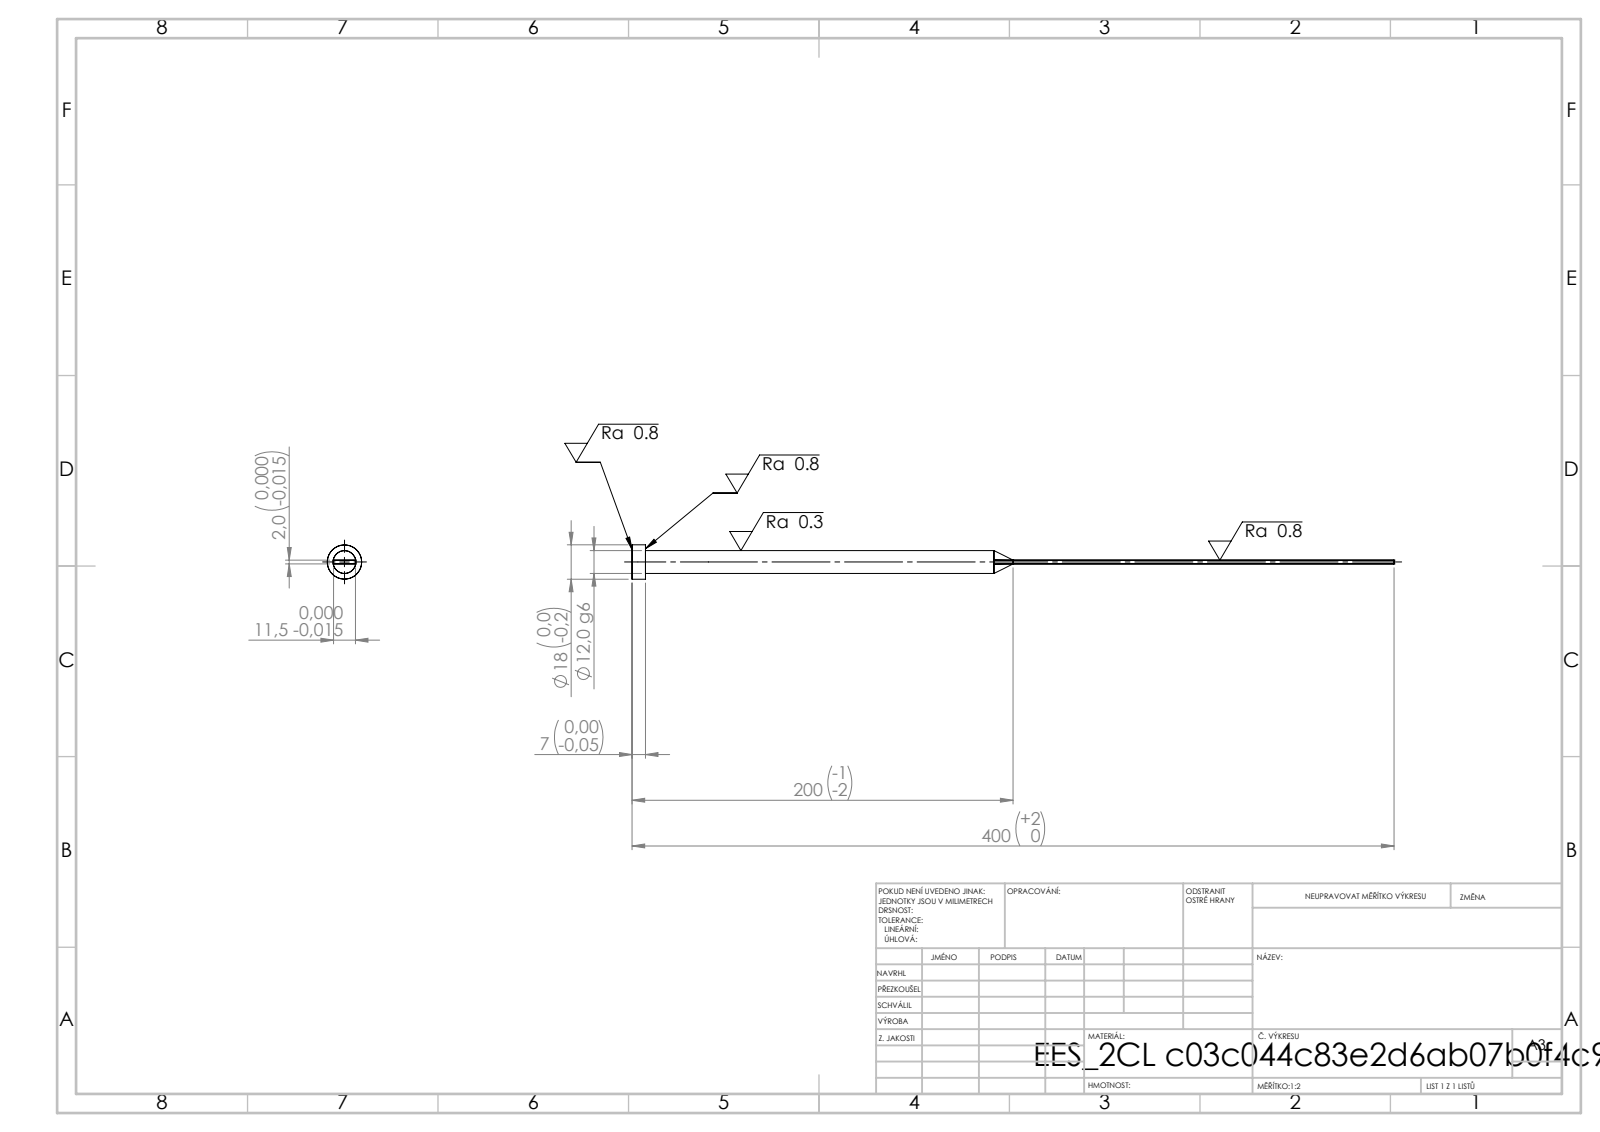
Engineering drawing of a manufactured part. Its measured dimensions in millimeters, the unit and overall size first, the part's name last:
Units: millimetres
Overall size (bounding box): 400 × 18 × 18
Round bosses / shafts (diameter × count): ⌀18 ×1, ⌀12 ×1
Main face-to-face distances: 2, 11.5, 7, 400, 393
Volume: 27 724 mm³ · Surface area: 13 439 mm²
Bodies: 1 solid, 15 faces (7 planar, 4 cylindrical, 4 other)
STEP written by: SolidWorks 2019 (CONFIG_CONTROL_DESIGN)
